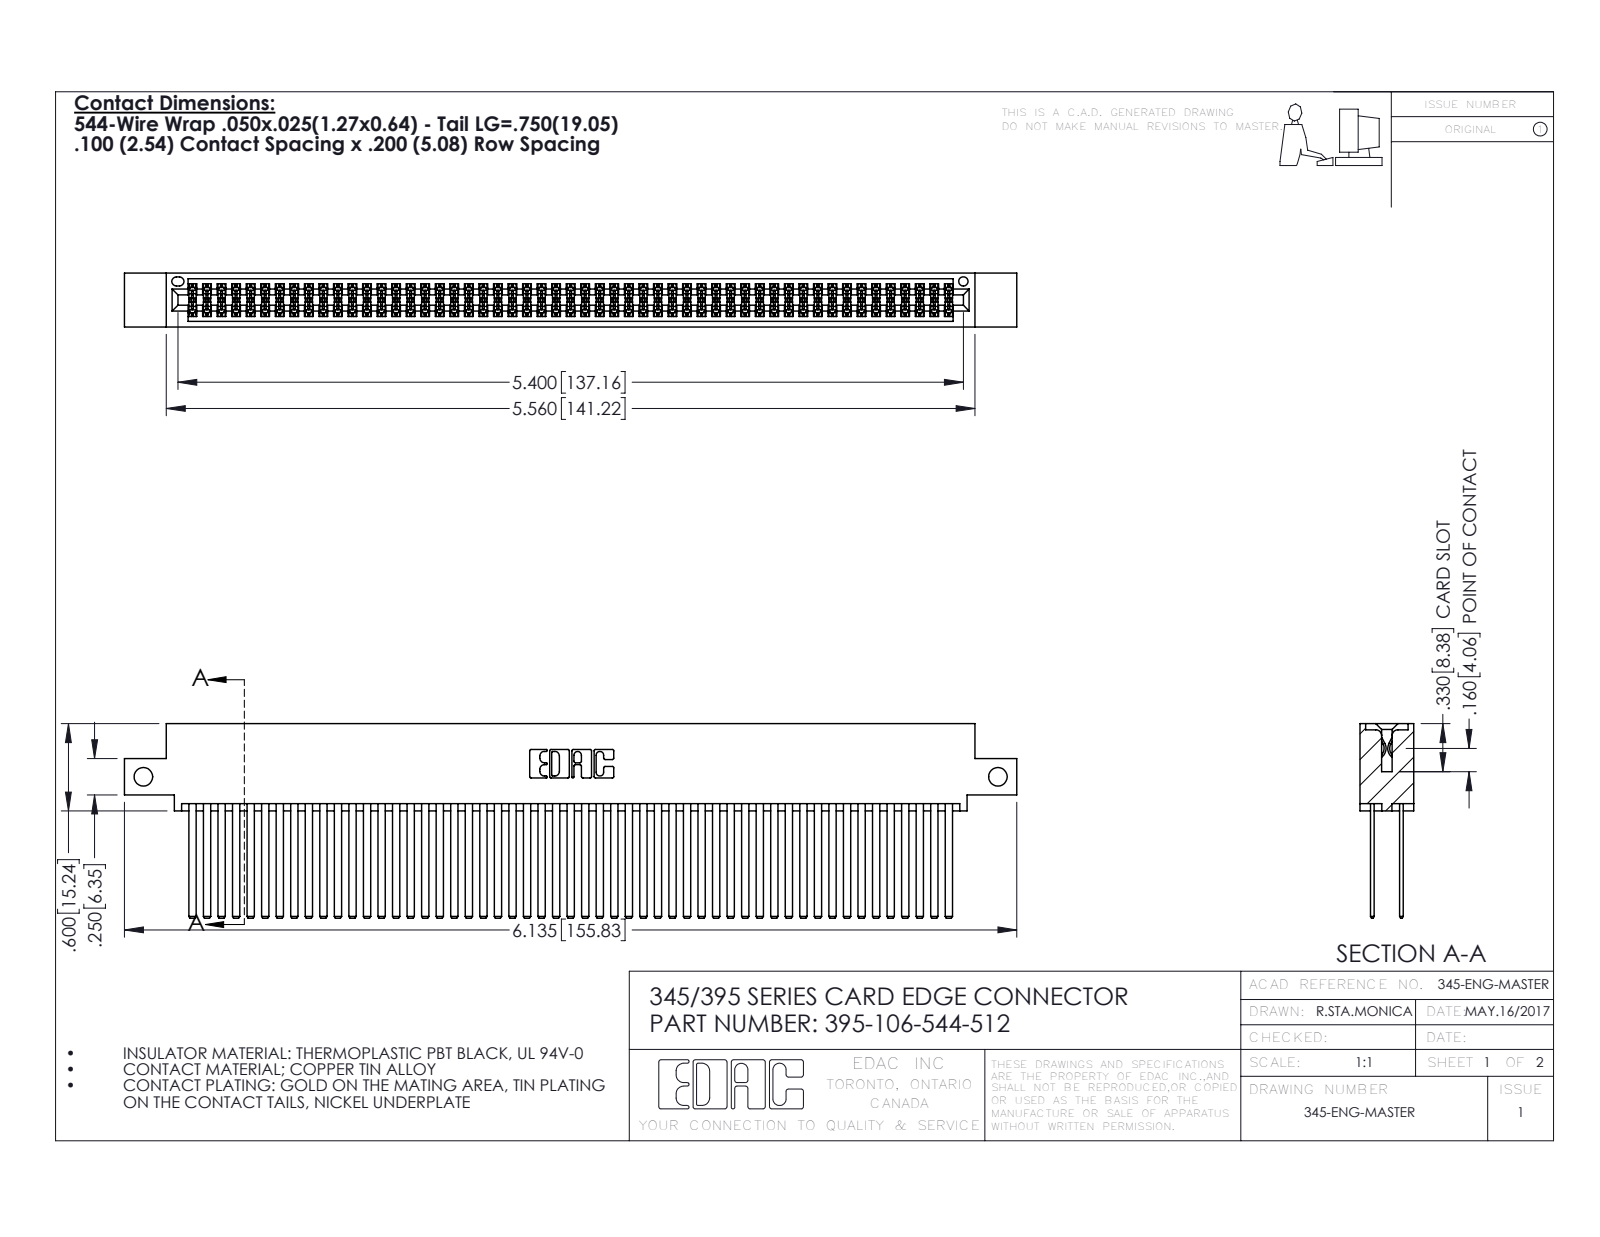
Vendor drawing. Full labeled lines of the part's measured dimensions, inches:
Part name (STEP PRODUCT): 345 Part_0.110 Offset - Side Mount; 395-106-544-512; 345-292-001_345-293-144
STEP written by: SolidWorks 2016 (CONFIG_CONTROL_DESIGN)
Units: inches
Bodies: 107 solids, 4794 faces (3158 planar, 1636 cylindrical, 0 other)
Overall size (bounding box): 6.135 × 1.337 × 0.37
Volume: 1.011 in³ · Surface area: 44.97 in²
Round holes (diameter × count): ⌀0.128 ×2, ⌀0.064 ×1
Partial cylindrical surfaces — rounded edges, fillets, slot ends (radius × count): R0.006 ×159, R0.01 ×22, R0.007 ×6, R0.031 ×6, R0.026 ×3, R0.014 ×2, R0.019 ×2, R0.022 ×2
Main face-to-face distances: 0.2, 0.025, 0.298, 0.072, 0.098, 0.272, 0.225, 0.175, 0.37, 0.05
Hole centre spacings: 5.875
